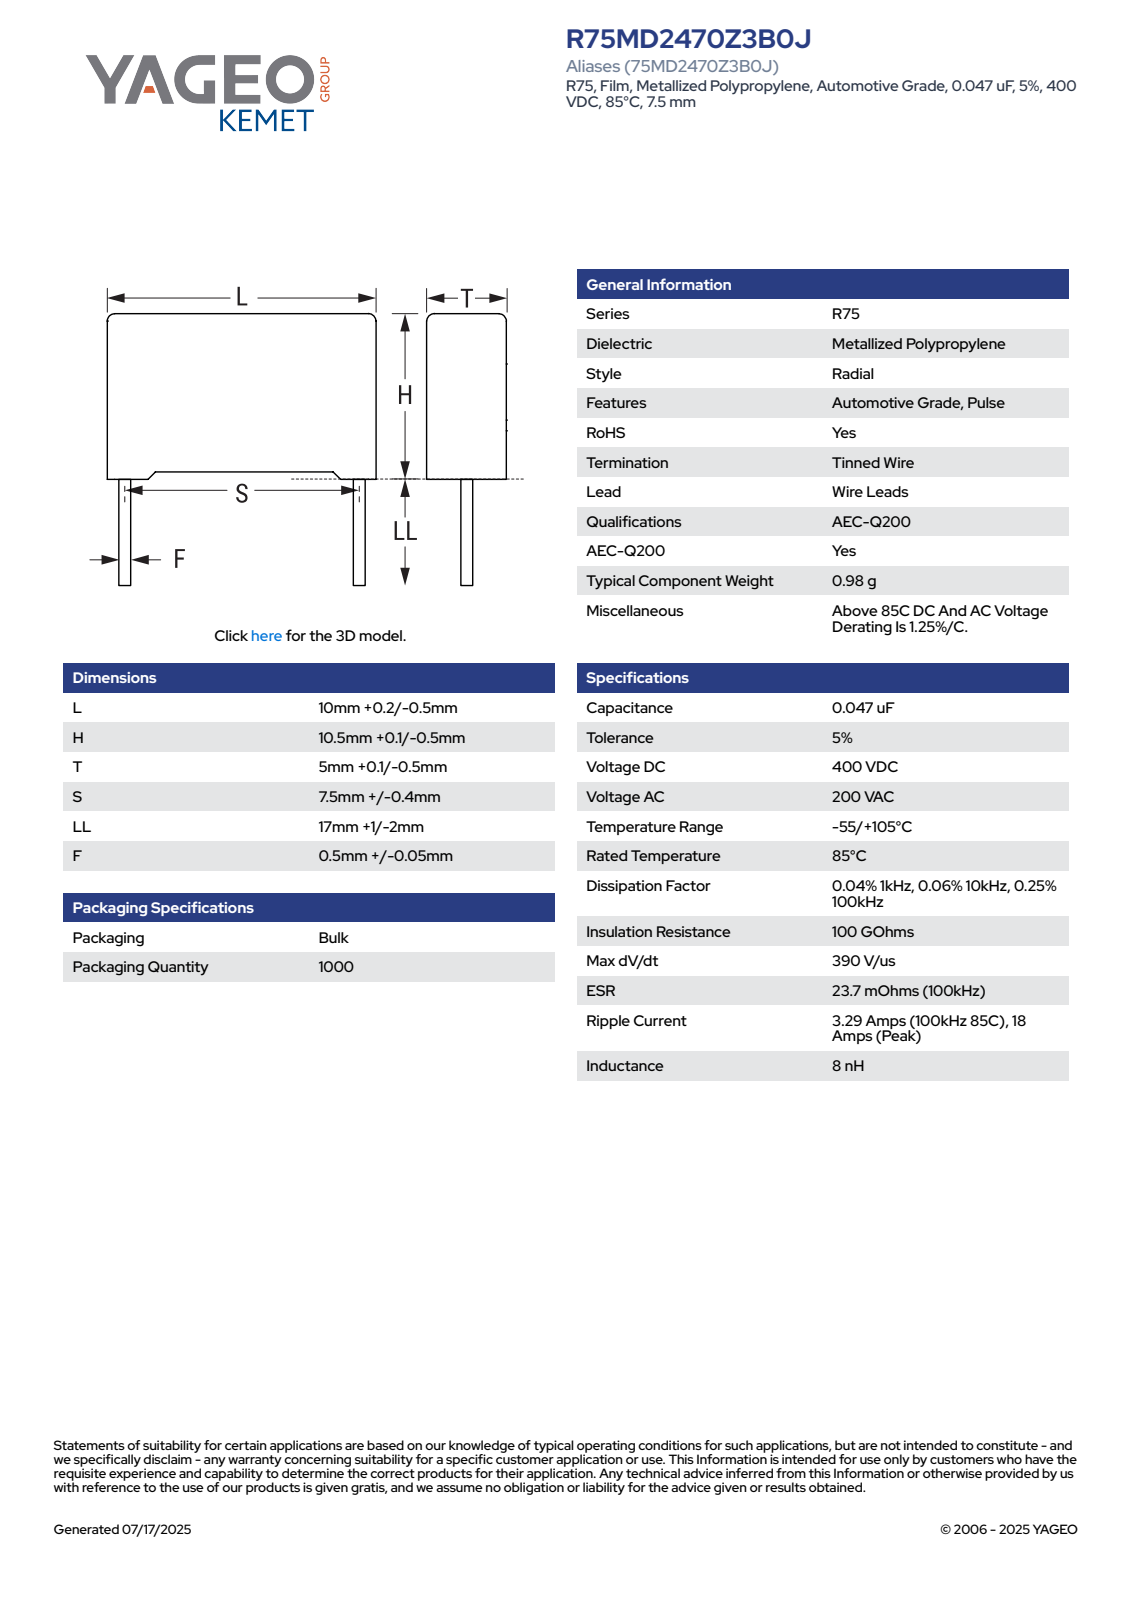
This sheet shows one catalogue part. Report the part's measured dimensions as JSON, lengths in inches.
{"part_name": "CFR_RB2_10X10.5X5_L10.2H10.6T5.1S7.5LL18F0.55", "step_written_by": "SolidWorks 2021 (AUTOMOTIVE_DESIGN)", "units": "inches", "bodies": {"solids": 4, "faces": 85, "planar": 77, "cylindrical": 8, "other": 0}, "overall_size": [1.126, 0.402, 0.201], "volume_in3": 0.032, "surface_area_in2": 0.789, "round_bosses_or_shafts": [[0.022, 2]], "partial_cylinders_radius": [[0.02, 4]], "face_to_face_distances": [0.201, 0.402, 0.388, 0.013, 0.187, 0.03, 0.417, 0.388, 0.174, 0.375]}
